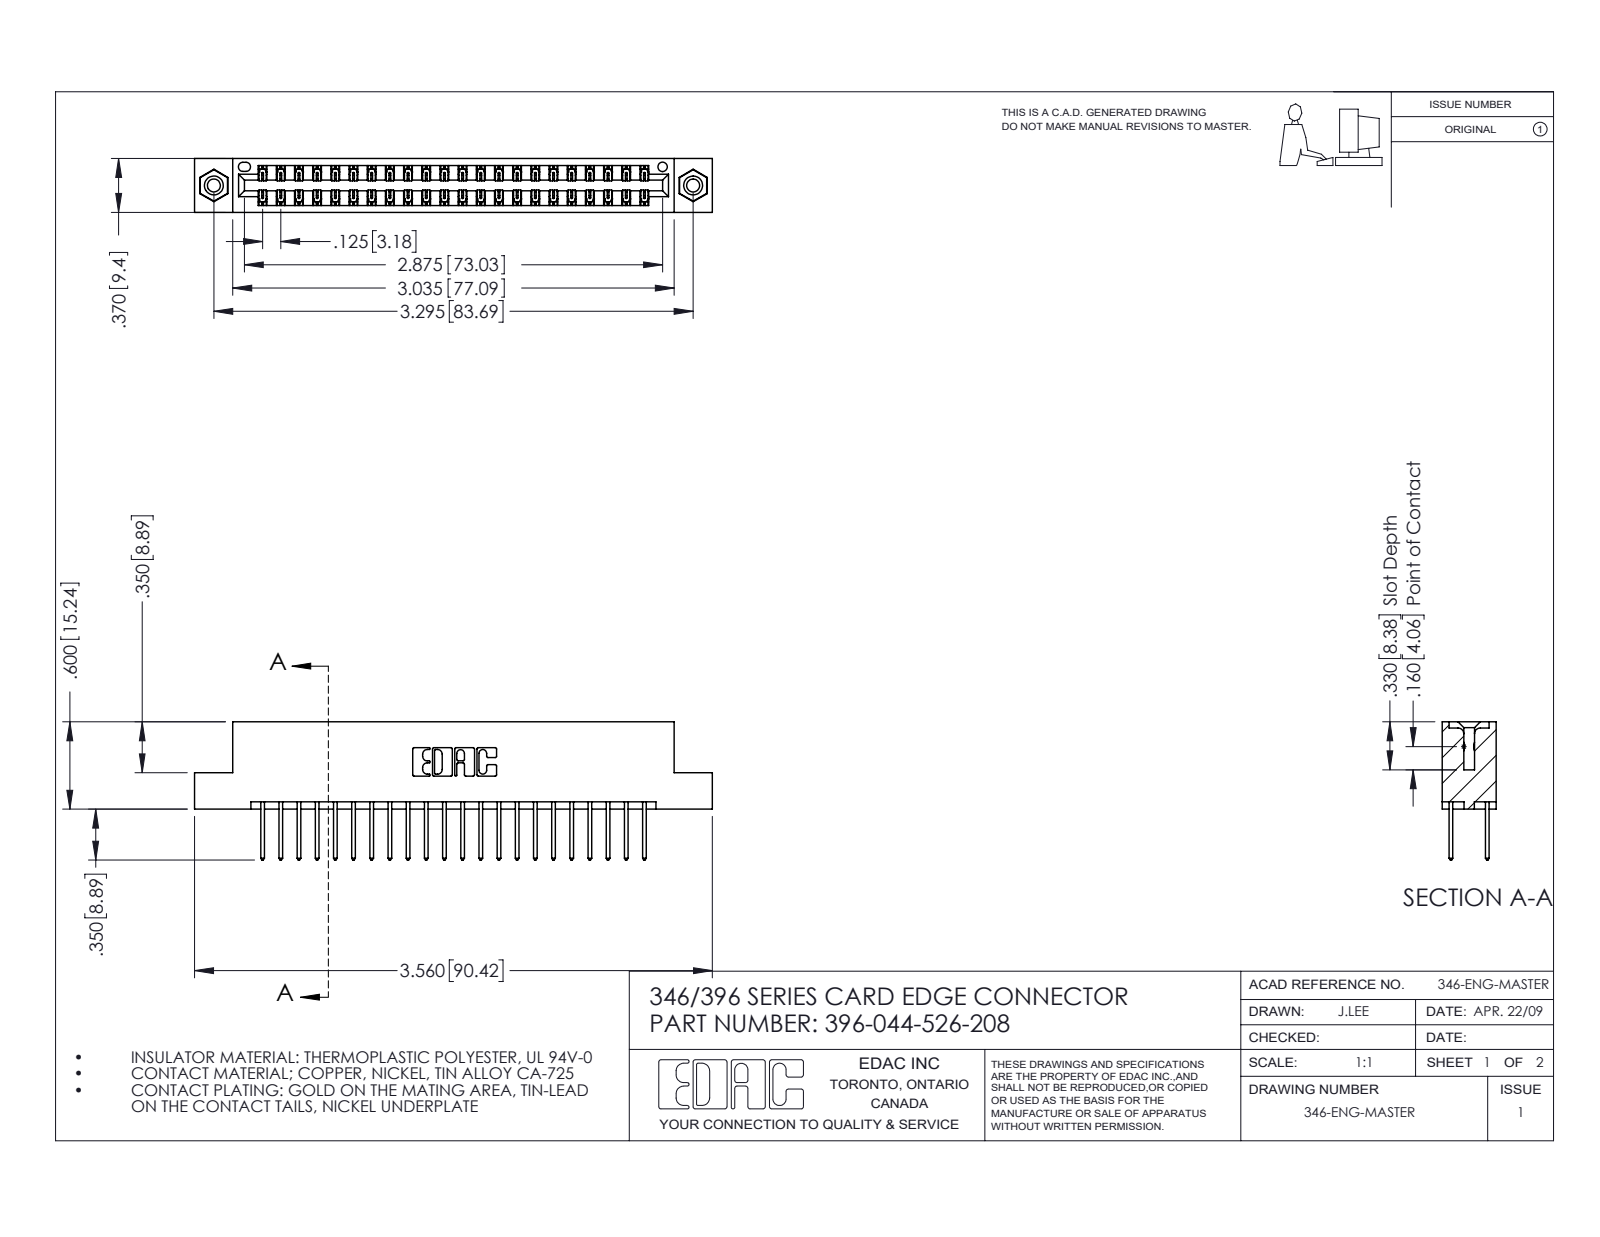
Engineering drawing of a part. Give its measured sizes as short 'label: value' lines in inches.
name: 346 Part_Flush Mounting Lugs - 0.156 Dia-TI; 345-250-001_345-250-003-102; 396-044-526-208; 345-292-001_345-293-126
written by: SolidWorks 2016 (CONFIG_CONTROL_DESIGN)
unit: in
bodies: 47 solids, 2470 faces (1648 planar, 806 cylindrical, 16 other)
size: 3.56 × 0.95 × 0.37
volume: 0.533 in³; area: 18.64 in²
holes: 2× ⌀0.089, 2× ⌀0.125, 2× ⌀0.156, 1× ⌀0.064
bosses: 2× ⌀0.155
rounds: 66× R0.006, 44× R0.01, 22× R0.01, 6× R0.007, 6× R0.031, 3× R0.026, 2× R0.014, 2× R0.022
face distances: 0.048, 0.322, 0.25, 0.37, 0.072, 0.298, 0.025, 0.275, 0.148, 0.222
hole spacings: 0.246, 3.087, 3.295
